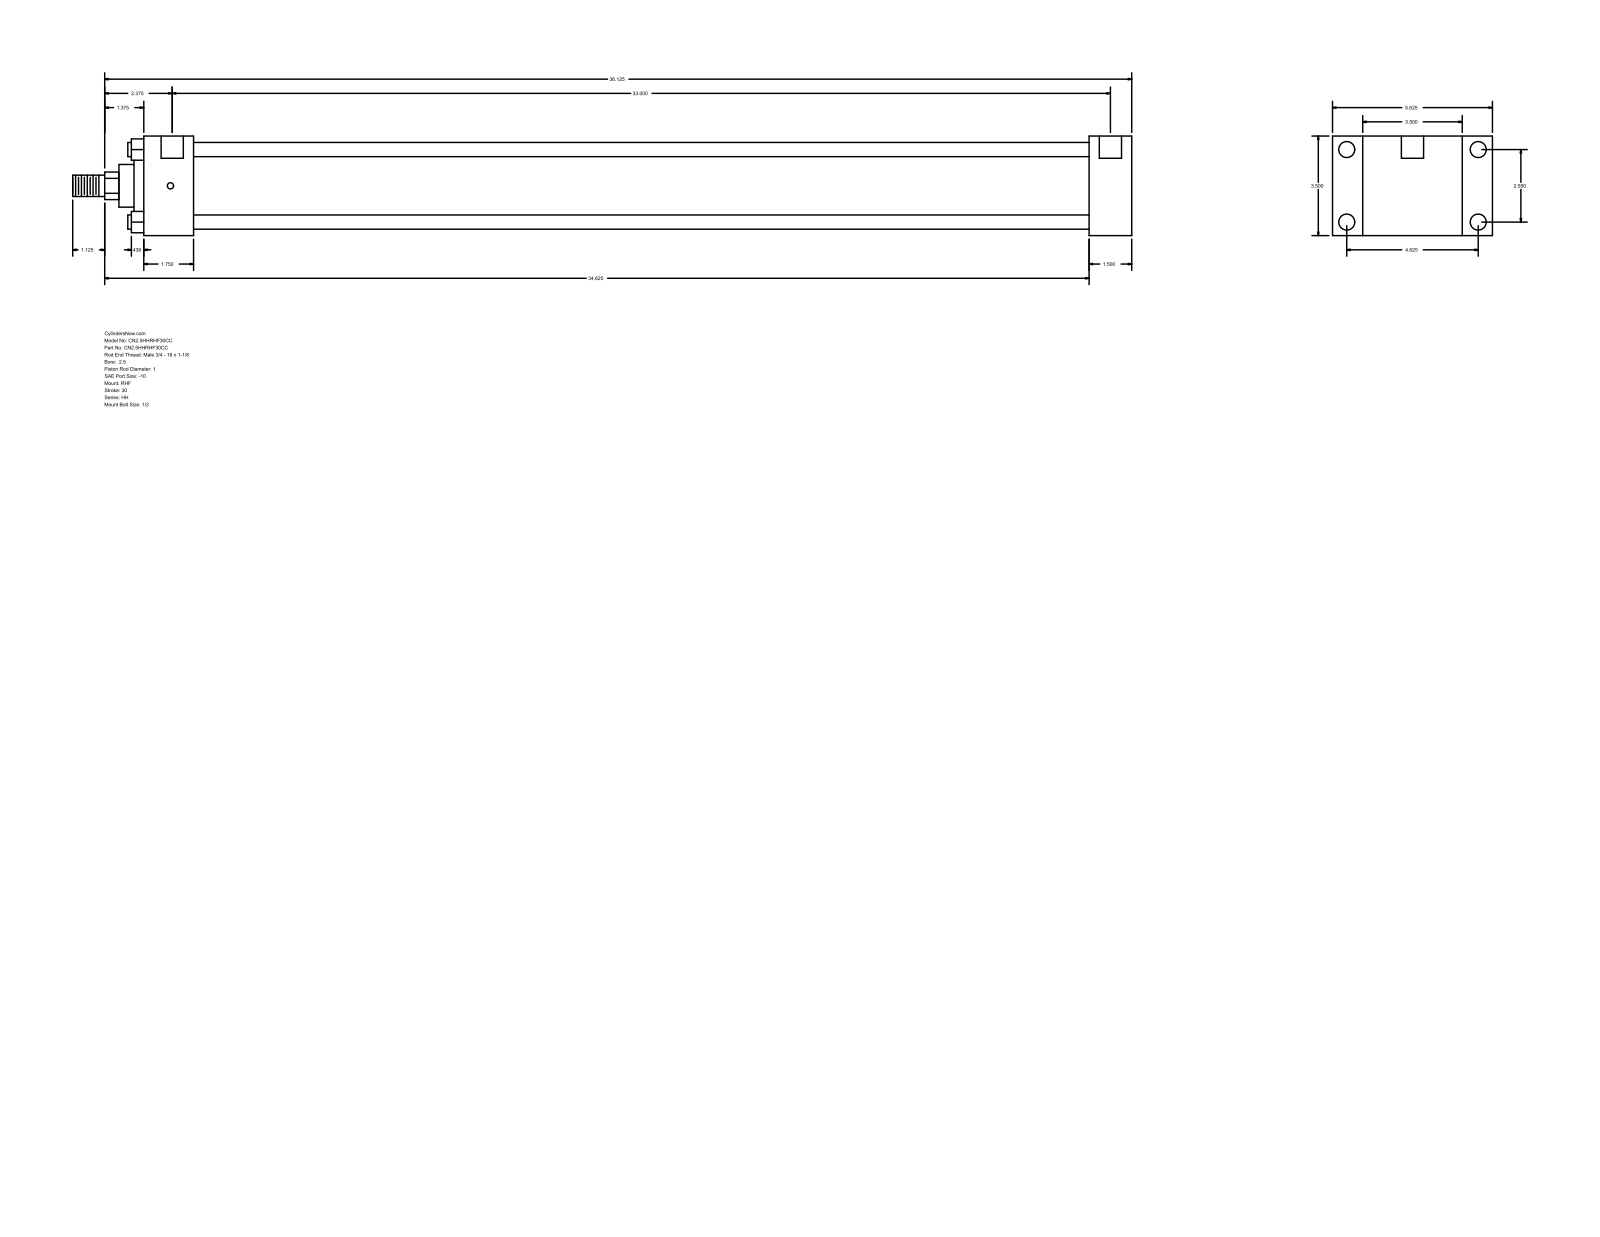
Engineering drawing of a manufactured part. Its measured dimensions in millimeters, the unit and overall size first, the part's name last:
Units: millimetres
Overall size (bounding box): 946.15 × 142.88 × 88.9
Round holes (diameter × count): ⌀5.56 ×4, ⌀14.3 ×4, ⌀19.84 ×2
Round bosses / shafts (diameter × count): ⌀12.7 ×4, ⌀73.03 ×1, ⌀60.33 ×1, ⌀38.1 ×1, ⌀25.4 ×1, ⌀19.05 ×1
Partial cylindrical surfaces — rounded edges, fillets, slot ends (radius × count): R12.29 ×1
Main face-to-face distances: 88.9, 38.1, 26.99, 115.89, 844.56, 882.66, 142.88, 44.46, 800.1, 838.2
Hole centre spacings: 1.59, 64.76, 117.48, 134.15, 839.78, 841.37, 838.19
Bodies: 0 solids, 90 faces (61 planar, 29 cylindrical, 0 other)
Part name (STEP PRODUCT): HH_RHF__0250_1
STEP written by: GSSL Pune (CONFIG_CONTROL_DESIGN)
